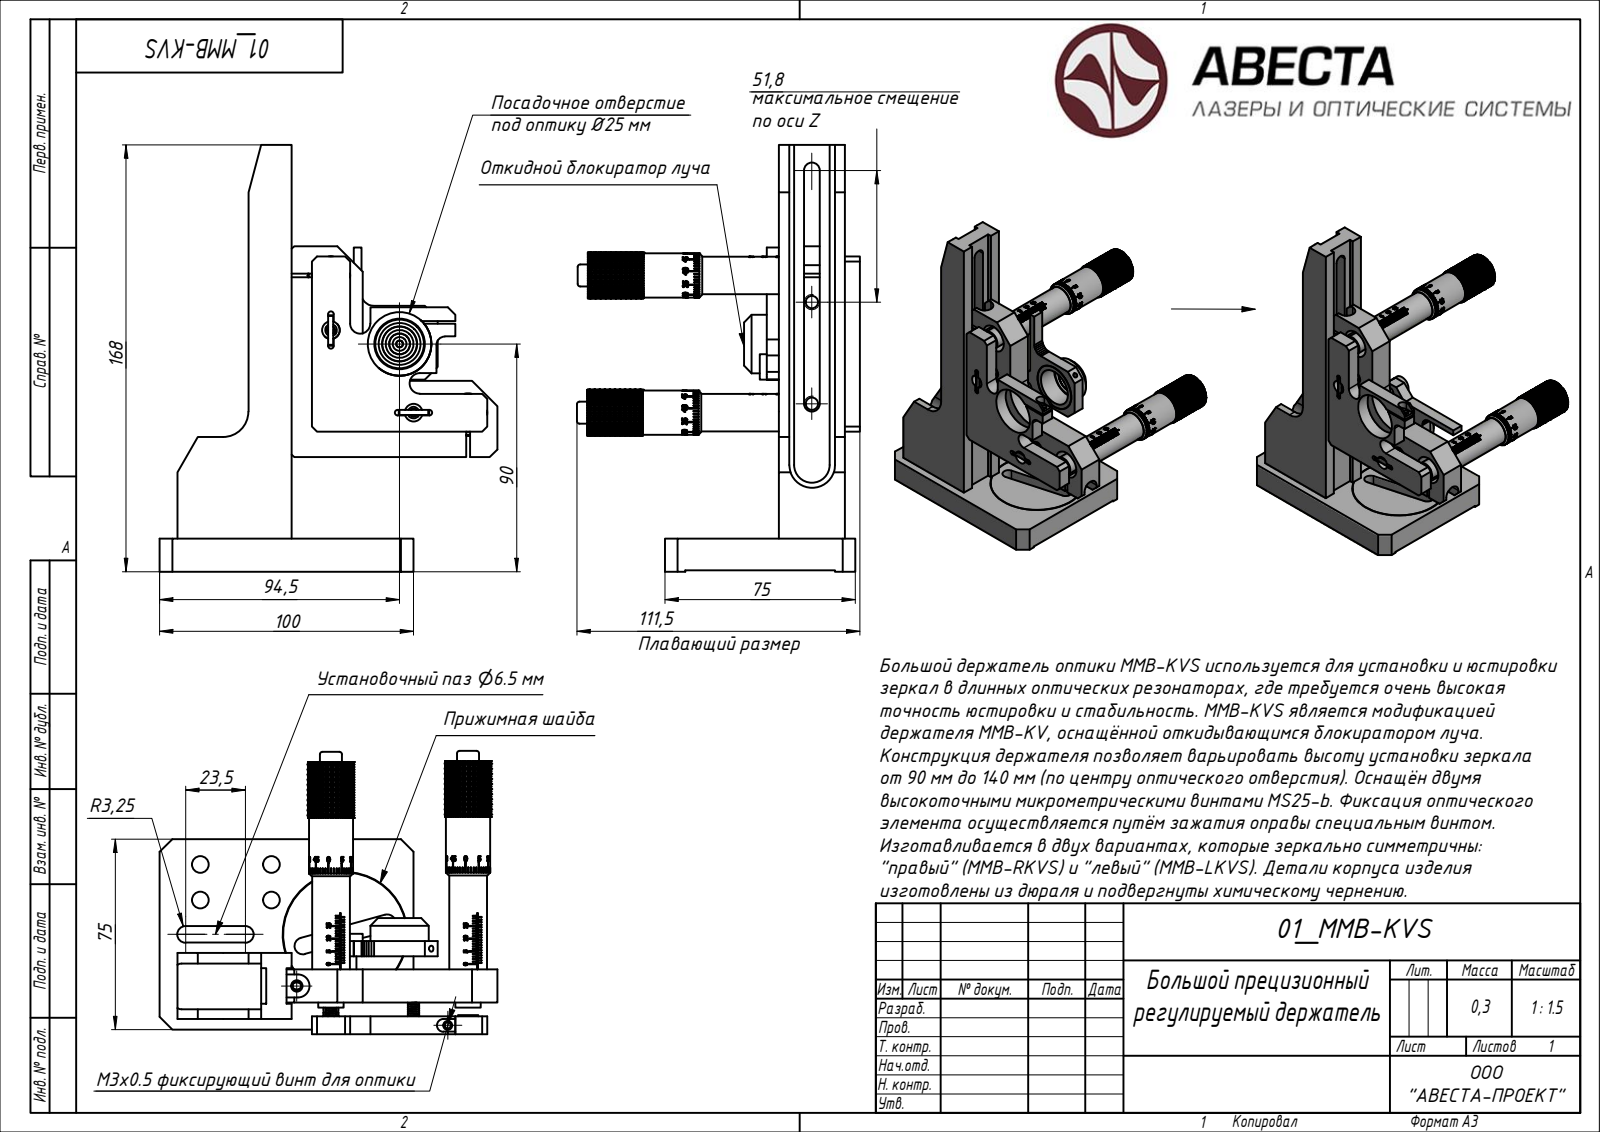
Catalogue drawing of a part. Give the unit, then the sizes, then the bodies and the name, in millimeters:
Units: millimetres
Overall size (bounding box): 168 × 133 × 99.89
Main face-to-face distances: 6.5, 19.5, 13, 10, 7, 26, 12.5, 20, 8, 0.5
Volume: 244 253 mm³ · Surface area: 88 774 mm²
Bodies: 20 solids, 501 faces (213 planar, 0 cylindrical, 288 other)
STEP written by: ST-DEVELOPER v15 (AUTOMOTIVE_DESIGN)
